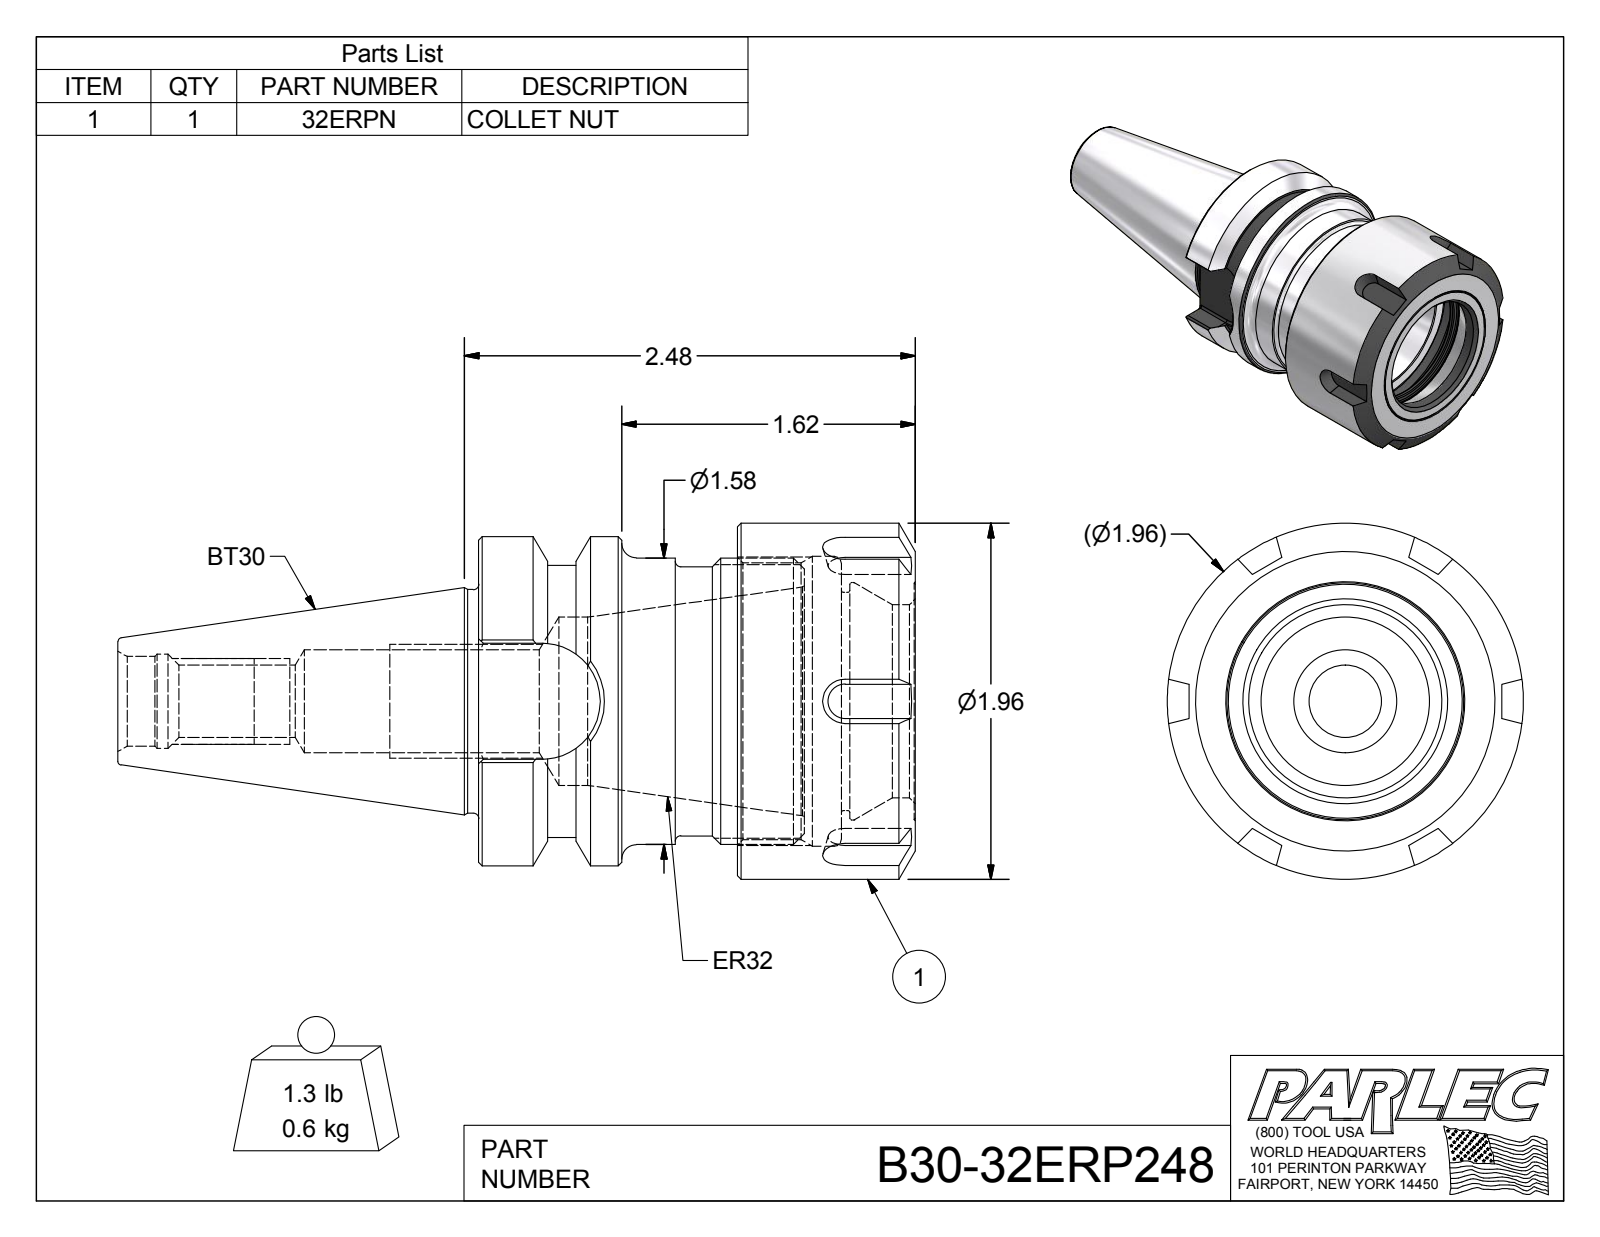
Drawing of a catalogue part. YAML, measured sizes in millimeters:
part_name: "B30-32ERP248; B30-32ER236-1; 32ERPN"
step_written_by: "Autodesk Inventor 2012 (AUTOMOTIVE_DESIGN)"
units: millimeters
bodies: {solids: 2, faces: 122, planar: 47, cylindrical: 30, other: 45}
overall_size: [105.5, 49.7, 49.7]
volume: 77350
surface_area: 27320
round_holes:
  - {diameter: 10.1, count: 1}
  - {diameter: 12.5, count: 1}
  - {diameter: 13.1, count: 1}
  - {diameter: 14.4, count: 1}
  - {diameter: 23.5, count: 1}
  - {diameter: 27, count: 1}
  - {diameter: 30.5, count: 1}
  - {diameter: 33.1, count: 1}
  - {diameter: 38.7, count: 1}
  - {diameter: 40.5, count: 1}
round_bosses_or_shafts:
  - {diameter: 49.7, count: 1}
  - {diameter: 46, count: 1}
  - {diameter: 40, count: 1}
  - {diameter: 40, count: 1}
  - {diameter: 37.6, count: 1}
  - {diameter: 31.2, count: 1}
partial_cylinders:
  - {radius: 0.5, count: 8}
  - {radius: 8.1, count: 1}
  - {radius: 19, count: 1}
face_to_face_distances: [24.8, 30.3, 55.1, 44.8, 14.5, 10.3, 45.5, 15.2, 0.7, 9.6]
